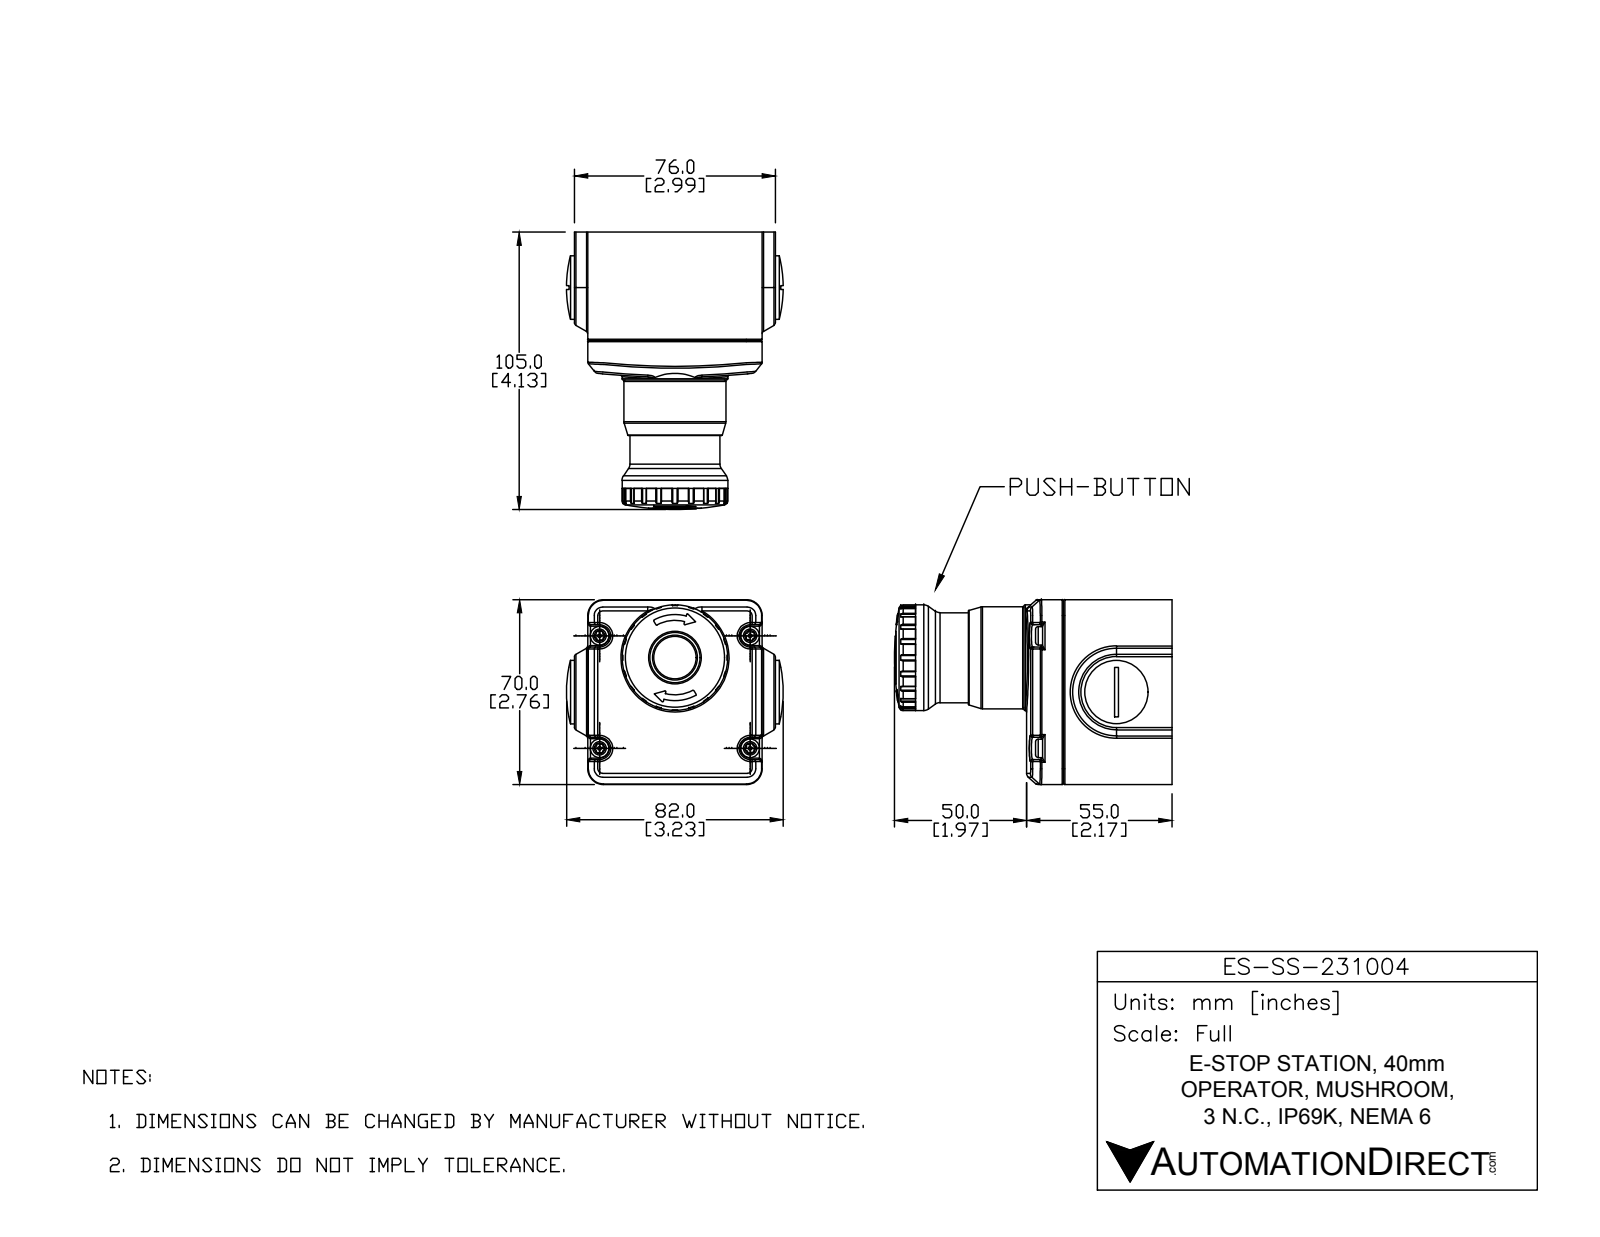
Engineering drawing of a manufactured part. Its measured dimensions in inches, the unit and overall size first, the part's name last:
Units: inches
Overall size (bounding box): 4.134 × 3.228 × 2.756
Round holes (diameter × count): ⌀0.173 ×4, ⌀1.224 ×1, ⌀1.457 ×1
Round bosses / shafts (diameter × count): ⌀0.276 ×4, ⌀0.039 ×4, ⌀1.575 ×1, ⌀1.52 ×1, ⌀1.339 ×1, ⌀0.945 ×1
Partial cylindrical surfaces — rounded edges, fillets, slot ends (radius × count): R0.004 ×80, R0.03 ×24, R0.02 ×14, R0.039 ×8, R0.008 ×4, R0.165 ×4, R0.236 ×4, R0.079 ×2
Main face-to-face distances: 1.614, 0.197, 2.795, 2.756, 2.205, 0.591, 2.992, 2.598, 2.236, 0.622
Hole centre spacings: 1.235, 1.966, 2.126, 2.283, 3.12
Volume: 17.37 in³ · Surface area: 78.85 in²
Bodies: 10 solids, 678 faces (213 planar, 250 cylindrical, 215 other)
Part name (STEP PRODUCT): ES-SS-231004
STEP written by: SolidWorks 2016 (AUTOMOTIVE_DESIGN)
